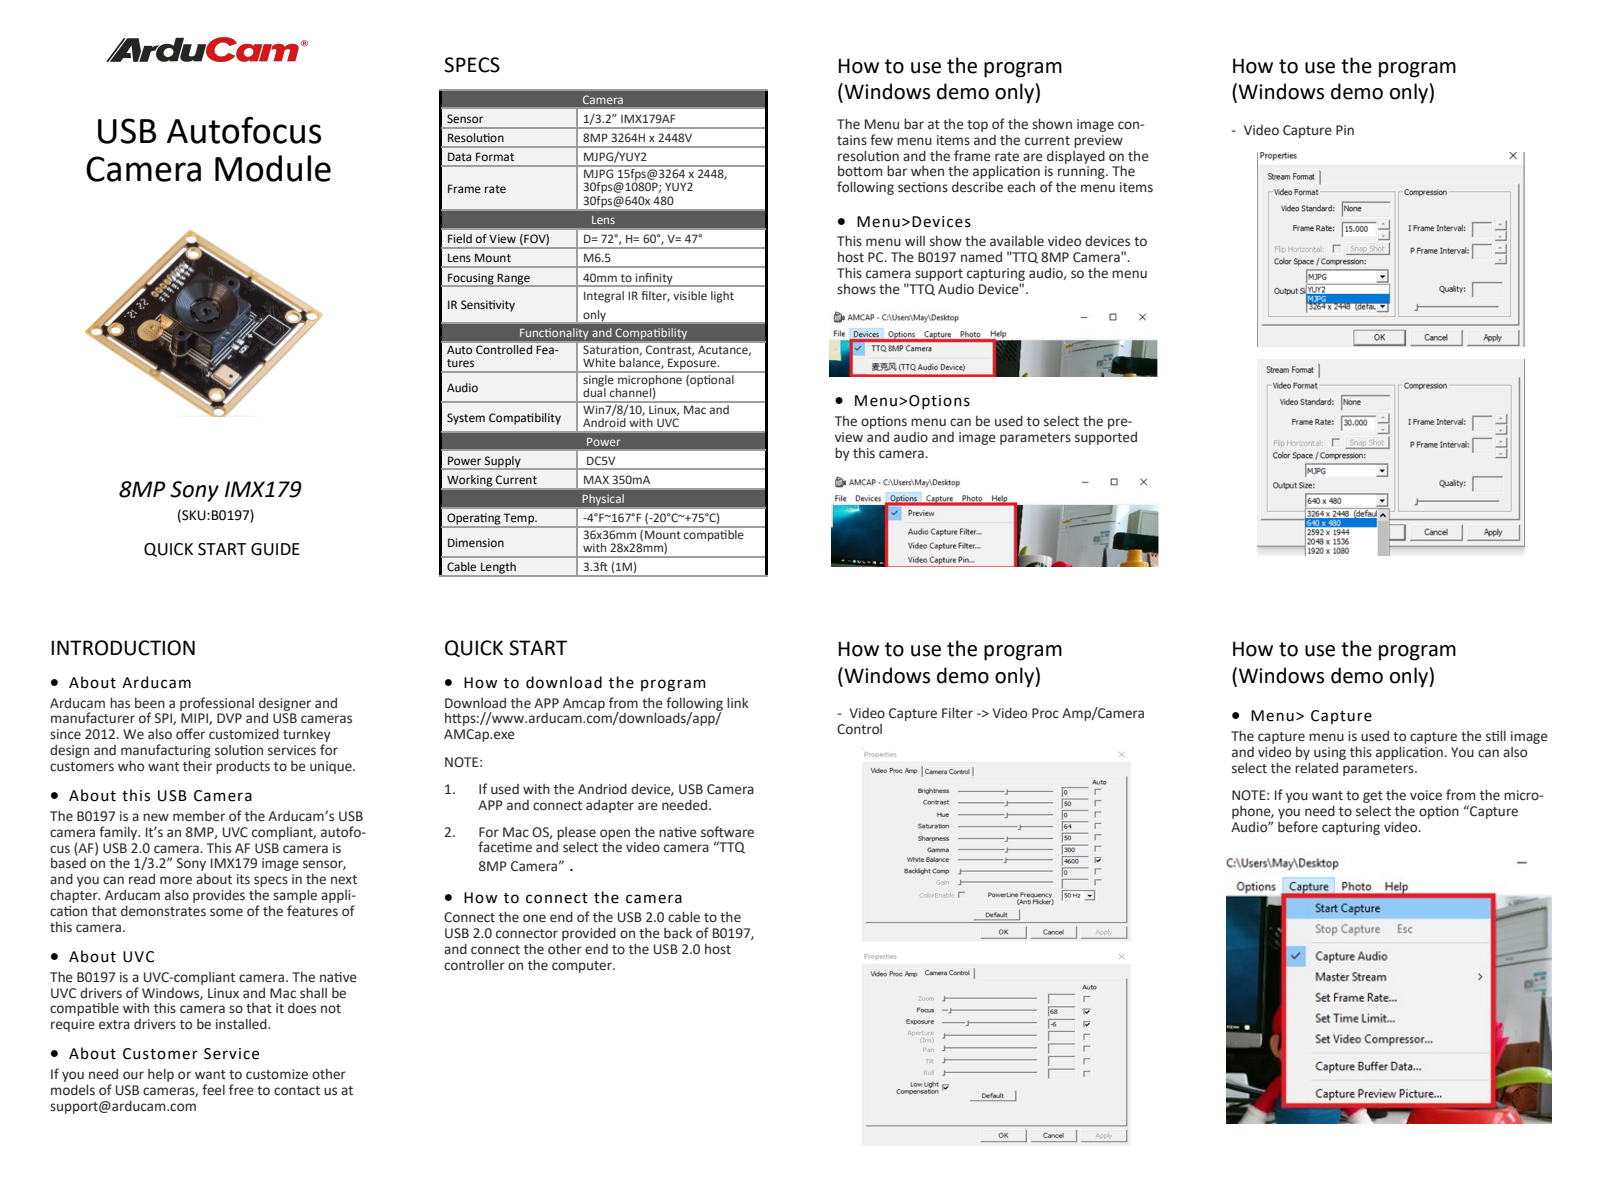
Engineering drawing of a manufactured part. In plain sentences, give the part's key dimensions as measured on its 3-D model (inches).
The part is named "B0197". Its 3-D file was written by "SolidWorks 2021 (AUTOMOTIVE_DESIGN)". It is 4 solids with 194 faces: 115 planar, 67 cylindrical and 12 other. Overall it measures 1.496 by 1.496 by 0.531 inches. Its volume is 0.17 cubic inches and its surface area 6.143 square inches. Round holes: 9 of diameter 0.118, 2 of diameter 0.059, 1 of diameter 0.02, 1 of diameter 0.053, 1 of diameter 0.276, 1 of diameter 0.366, 1 of diameter 0.382, 1 of diameter 0.398, 1 of diameter 0.413, 1 of diameter 0.429, 1 of diameter 0.445, 1 of diameter 0.461. Round bosses or shafts: 4 of diameter 0.02, 1 of diameter 0.571, 1 of diameter 0.236. Partial cylindrical surfaces (rounded edges, fillets, slot ends): 2 of radius 0.089, 1 of radius 0.133. The main face-to-face distances are 0.039, 0.463, 1.033, 0.571, 0.059, 0.335, 0.069, 0.128, 1.368, 1.427. The hole center spacings are 1.226, 0.167, 0.585, 0.74, 0.78, 0.946, 1.06, 1.102.
